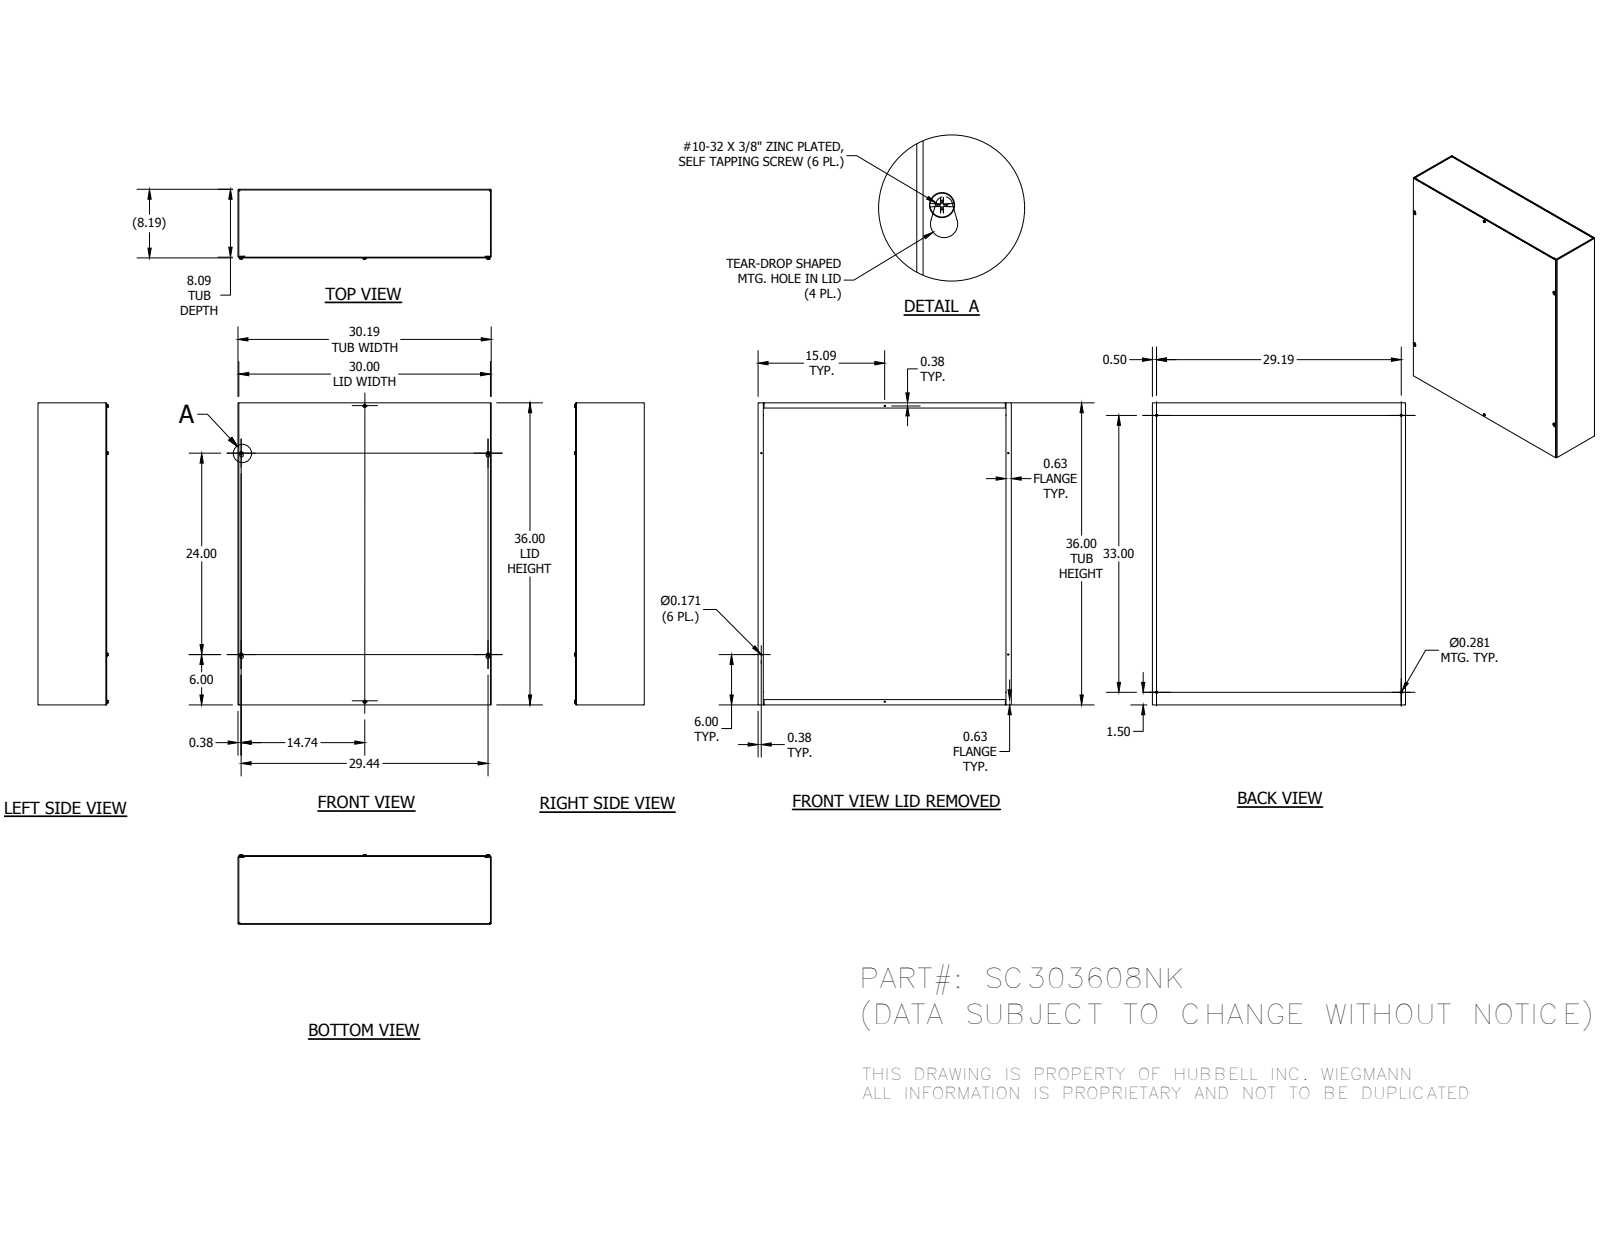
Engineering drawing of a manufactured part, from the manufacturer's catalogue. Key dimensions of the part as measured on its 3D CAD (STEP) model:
Part name (STEP PRODUCT): SC303608NKBLR; SC3008NKTB; SC3036LPA; 37214 (+1 more)
STEP written by: Autodesk Inventor 2014 (AUTOMOTIVE_DESIGN)
Units: millimetres
Bodies: 10 solids, 404 faces (232 planar, 50 cylindrical, 122 other)
Overall size (bounding box): 914.4 × 766.76 × 211.31
Volume: 5 118 000 mm³ · Surface area: 4 328 000 mm²
Round holes (diameter × count): ⌀4.34 ×6, ⌀7.14 ×4, ⌀7.92 ×2
Round bosses / shafts (diameter × count): ⌀4.83 ×6
Partial cylindrical surfaces — rounded edges, fillets, slot ends (radius × count): R0.4 ×12, R2.78 ×12, R3.17 ×4, R5.16 ×4
Main face-to-face distances: 2.38, 205.58, 203.2, 207.96, 764.38, 912.02, 762, 766.76, 914.4, 909.64
Hole centre spacings: 114.34, 371.78, 400.23, 723.91, 753.26, 840.23, 942.71, 1038.45
